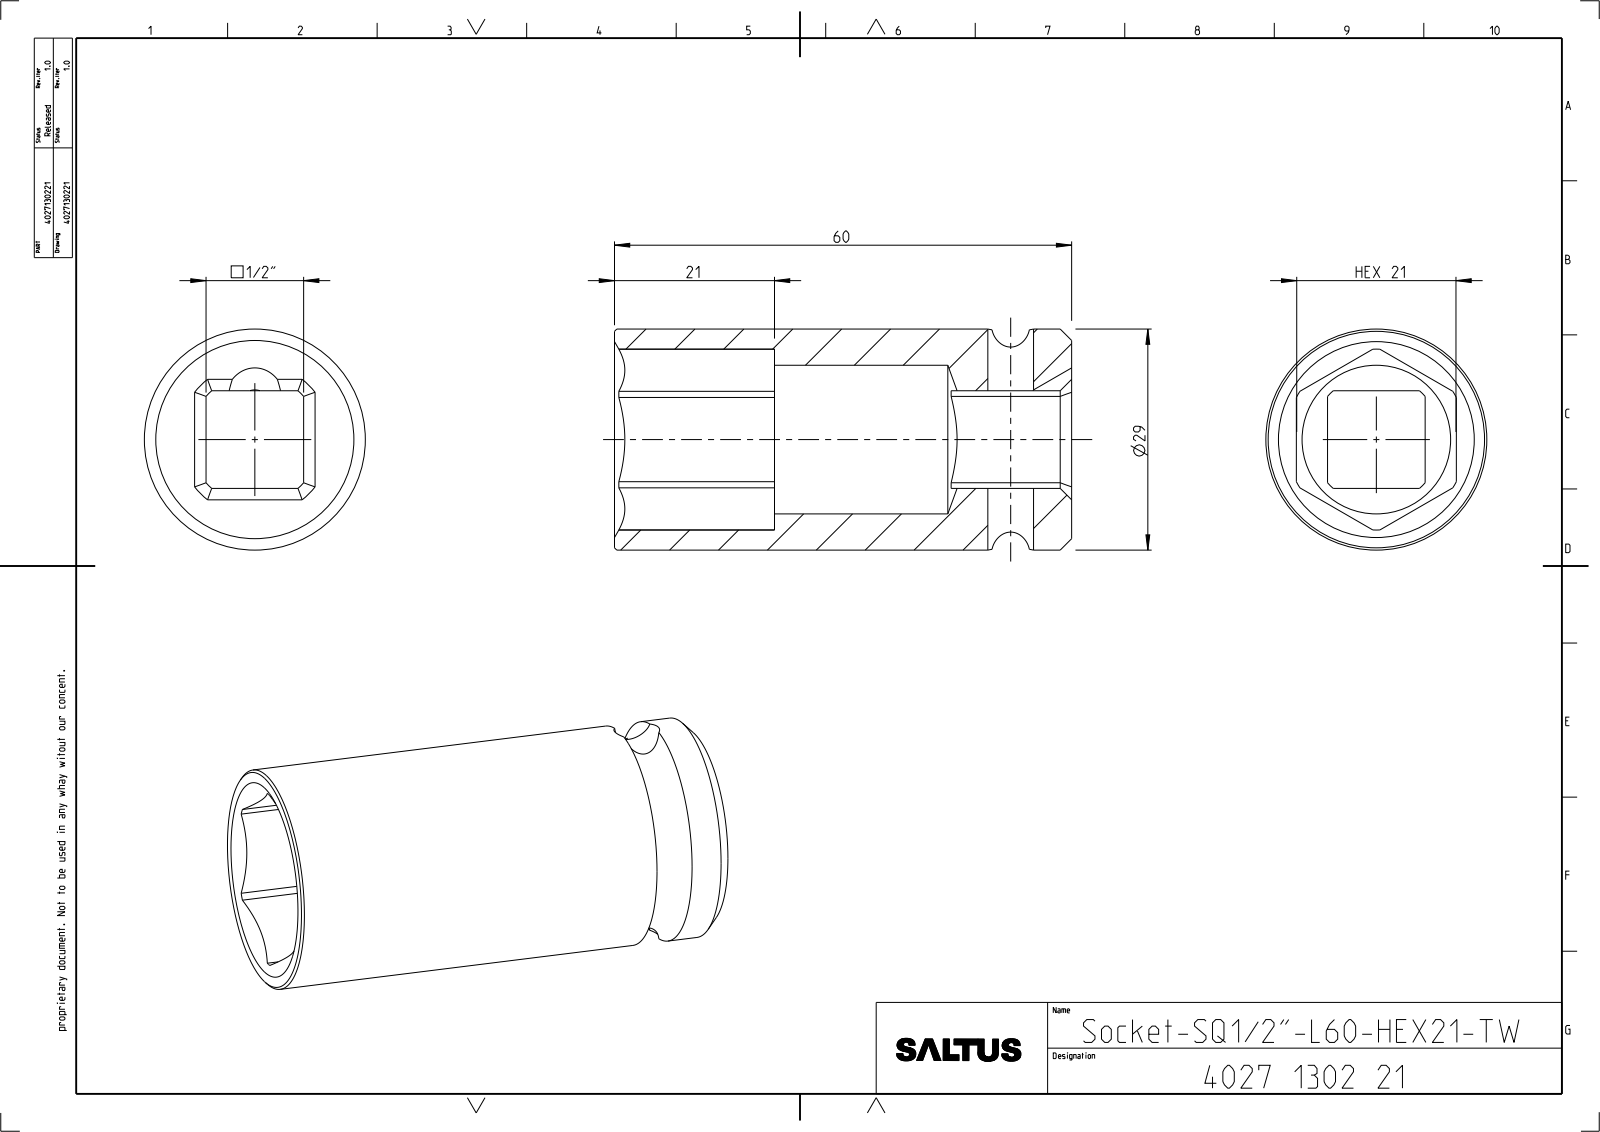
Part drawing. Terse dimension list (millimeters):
name: 4027130221
written by: CREO PARAMETRIC BY PTC INC, 2022414 (CONFIG_CONTROL_DESIGN)
unit: mm
bodies: 1 solid, 53 faces (18 planar, 21 cylindrical, 14 other)
size: 60 × 29 × 29
volume: 20 852 mm³; area: 10 196 mm²
holes: 1× ⌀6, 1× ⌀19.5
bosses: 1× ⌀29
rounds: 1× R4, 1× R8.55, 1× R11.87
face distances: 21, 4.09, 16.91, 12.82, 60, 39
